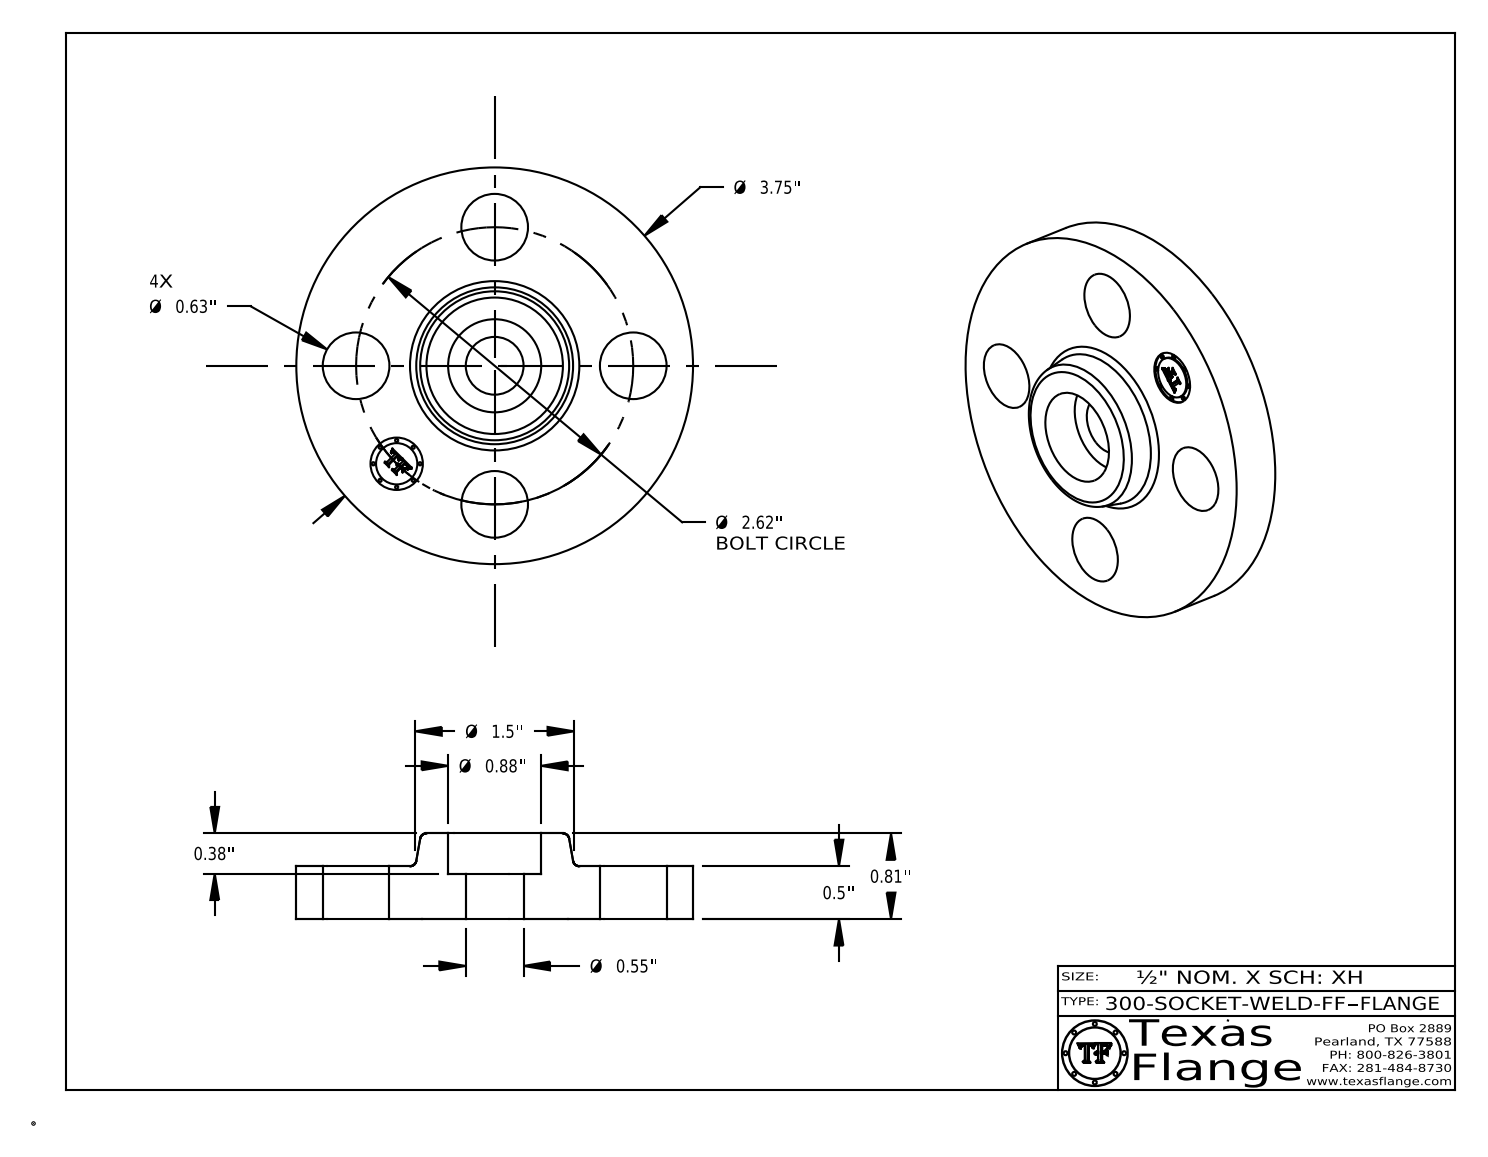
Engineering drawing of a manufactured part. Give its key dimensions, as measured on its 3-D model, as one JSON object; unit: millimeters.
{"part_name": "300-SOCKET-WELD-FF", "step_written_by": "CATIA V5 STEP AP214 (AUTOMOTIVE_DESIGN)", "units": "millimeters", "bodies": {"solids": 1, "faces": 410, "planar": 370, "cylindrical": 34, "other": 6}, "overall_size": [95.3, 95.3, 20.6], "volume_mm3": 83160, "surface_area_mm2": 20570, "round_holes": [[16, 4], [12.6, 1], [13.9, 1], [22.4, 1]], "round_bosses_or_shafts": [[0.8, 8], [95.3, 1], [9.9, 1]], "face_to_face_distances": [12.7, 20.6, 7.9, 1.8, 10.9, 9.7, 12.3, 1.4, 0.4, 8.3], "hole_center_spacings": [33.3, 47, 25.5, 61.5, 66.5, 33.3]}
